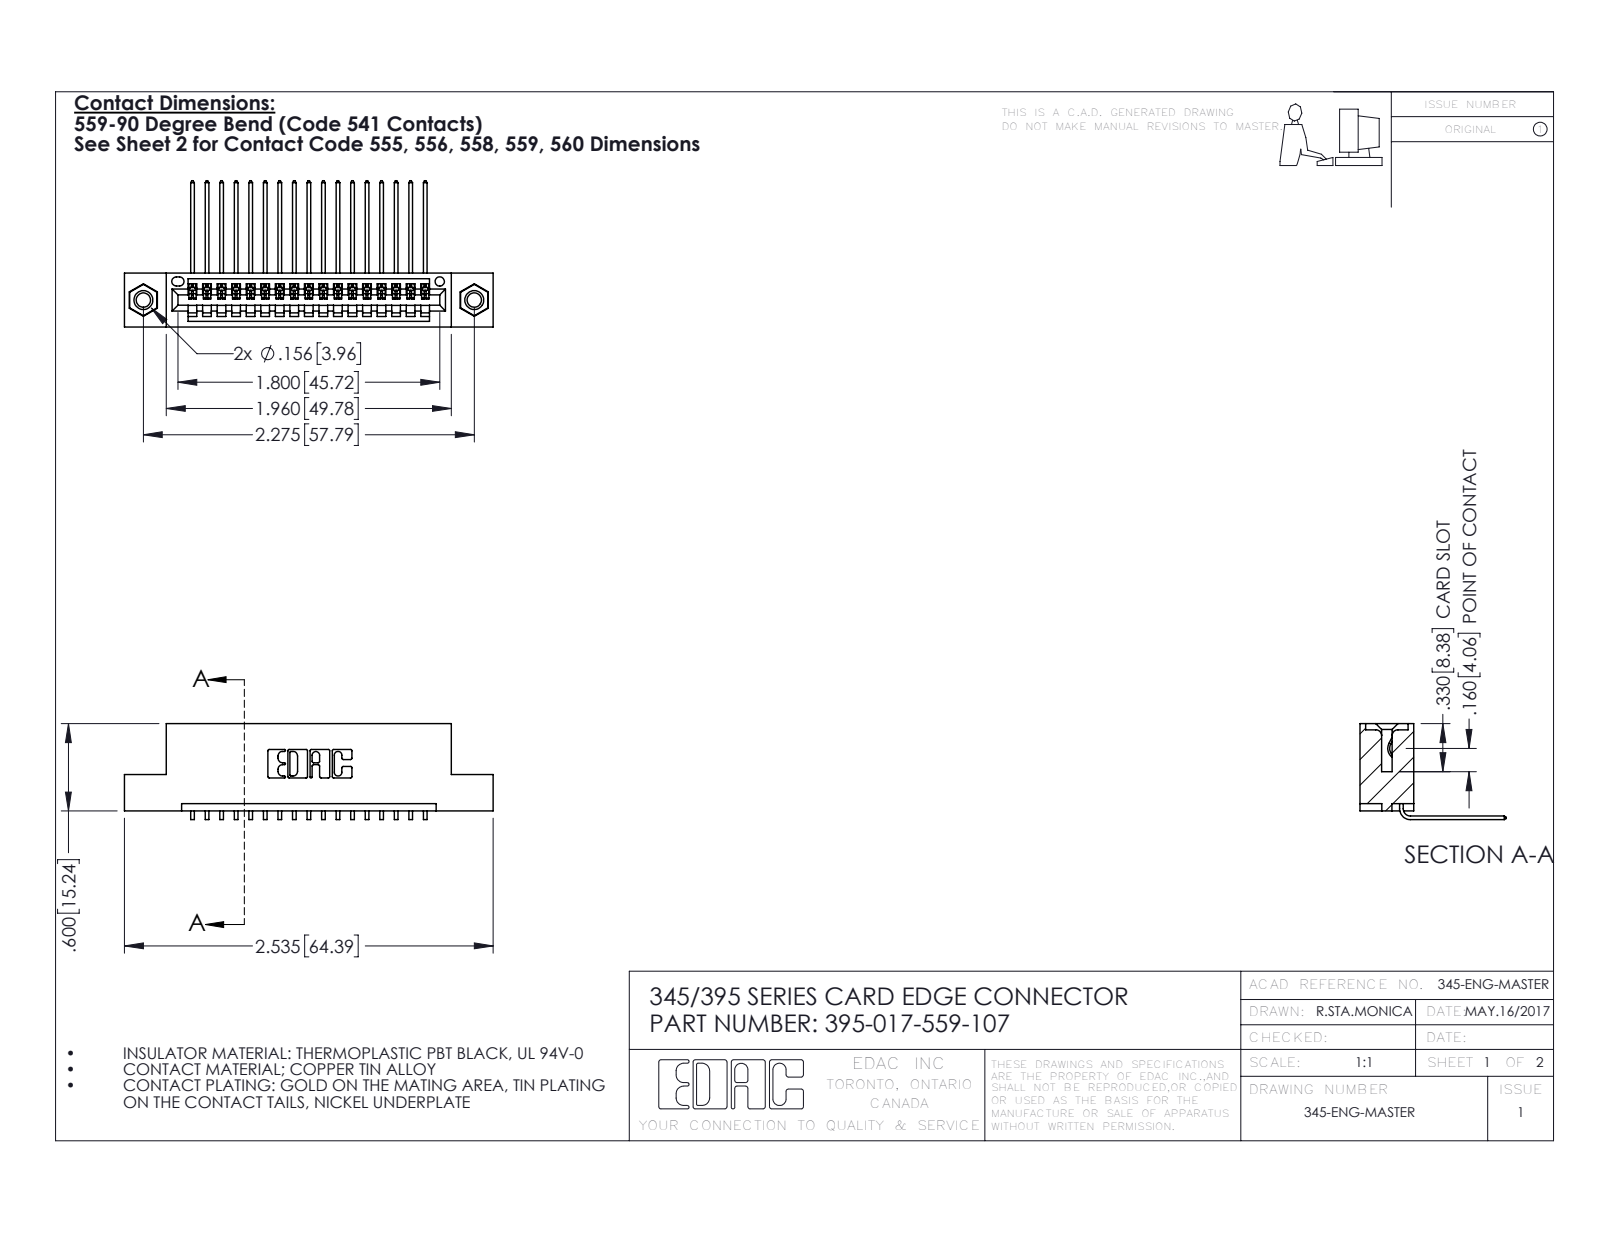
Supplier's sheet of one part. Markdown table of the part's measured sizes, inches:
| quantity | value |
| --- | --- |
| part name | 345 Part_Flush Mounting Lugs - 0.156 Dia-TI; 345-250-001_345-250-005-103; 345-292-001_558 559 Tail - 1; 395-017-559-107 |
| STEP written by | SolidWorks 2016 (CONFIG_CONTROL_DESIGN) |
| units | inches |
| bodies | 20 solids, 1206 faces (826 planar, 364 cylindrical, 16 other) |
| overall size | 2.535 × 1.005 × 0.659 |
| volume | 0.363 in³ |
| surface area | 12.3 in² |
| round holes (diameter × count) | 0.098 × 2, 0.125 × 2, 0.156 × 2, 0.064 × 1 |
| round bosses / shafts (diameter × count) | 0.155 × 2 |
| partial cylindrical surfaces (radius × count) | 0.006 × 34, 0.01 × 22, 0.007 × 6, 0.031 × 6, 0.026 × 3, 0.031 × 2, 0.04 × 2, 0.014 × 1 |
| main face-to-face distances | 0.072, 0.298, 0.2, 0.37, 0.098, 0.272, 0.025, 0.225, 0.1, 0.149 |
| hole center spacings | 0.27, 2.041, 2.275 |
